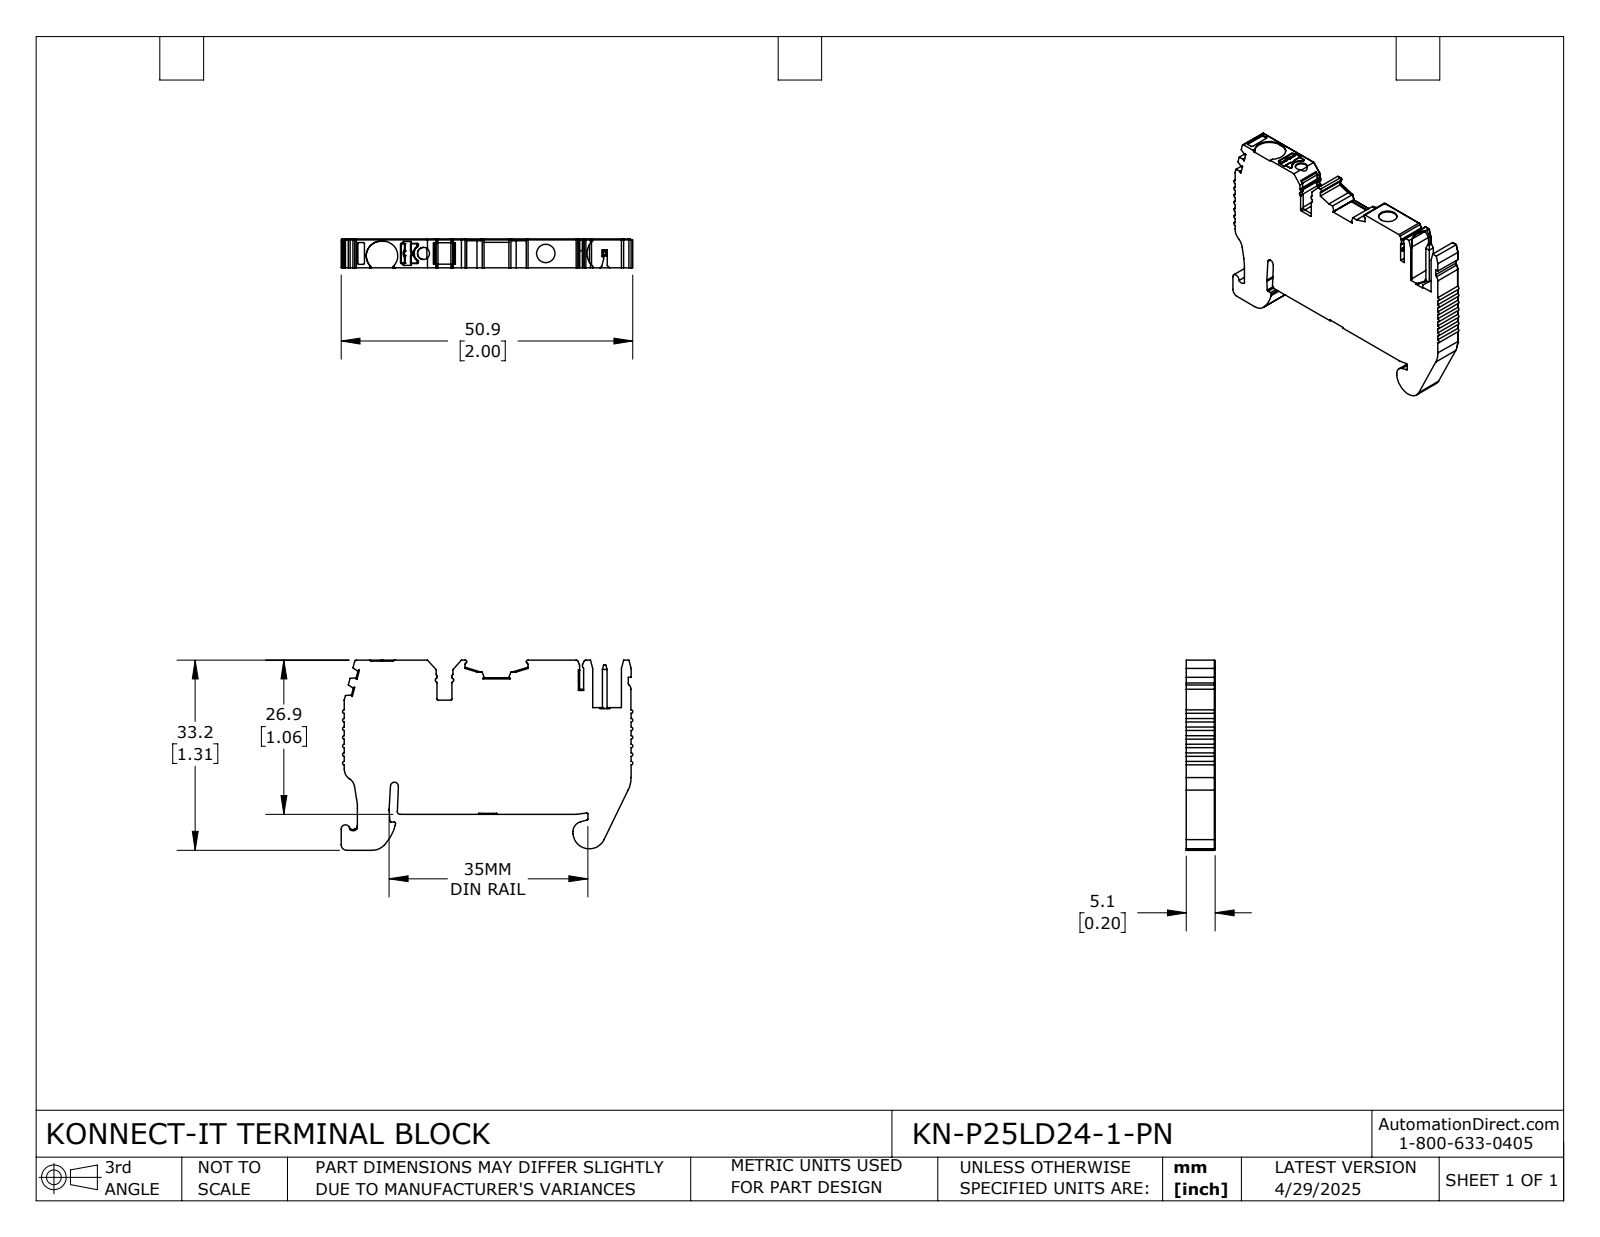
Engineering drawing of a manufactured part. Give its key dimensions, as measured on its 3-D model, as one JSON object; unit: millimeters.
{"part_name": "KN-P25LD24-1-PN", "step_written_by": "SolidWorks 2024 (CONFIG_CONTROL_DESIGN)", "units": "millimeters", "bodies": {"solids": 1, "faces": 461, "planar": 263, "cylindrical": 179, "other": 19}, "overall_size": [50.92, 33.21, 5.05], "volume_mm3": 6509, "surface_area_mm2": 3879, "round_holes": [[2.1, 1], [3.2, 1]], "partial_cylinders_radius": [[0.3, 35], [0.2, 34], [0.5, 13], [0.1, 9], [0.4, 8], [0.15, 4], [0.6, 3], [0.9, 3]], "face_to_face_distances": [5.05, 26.95, 26.75, 50.07, 48.38, 1.69, 24.91, 5.2, 43.18, 6.89], "hole_center_spacings": [21.35]}
